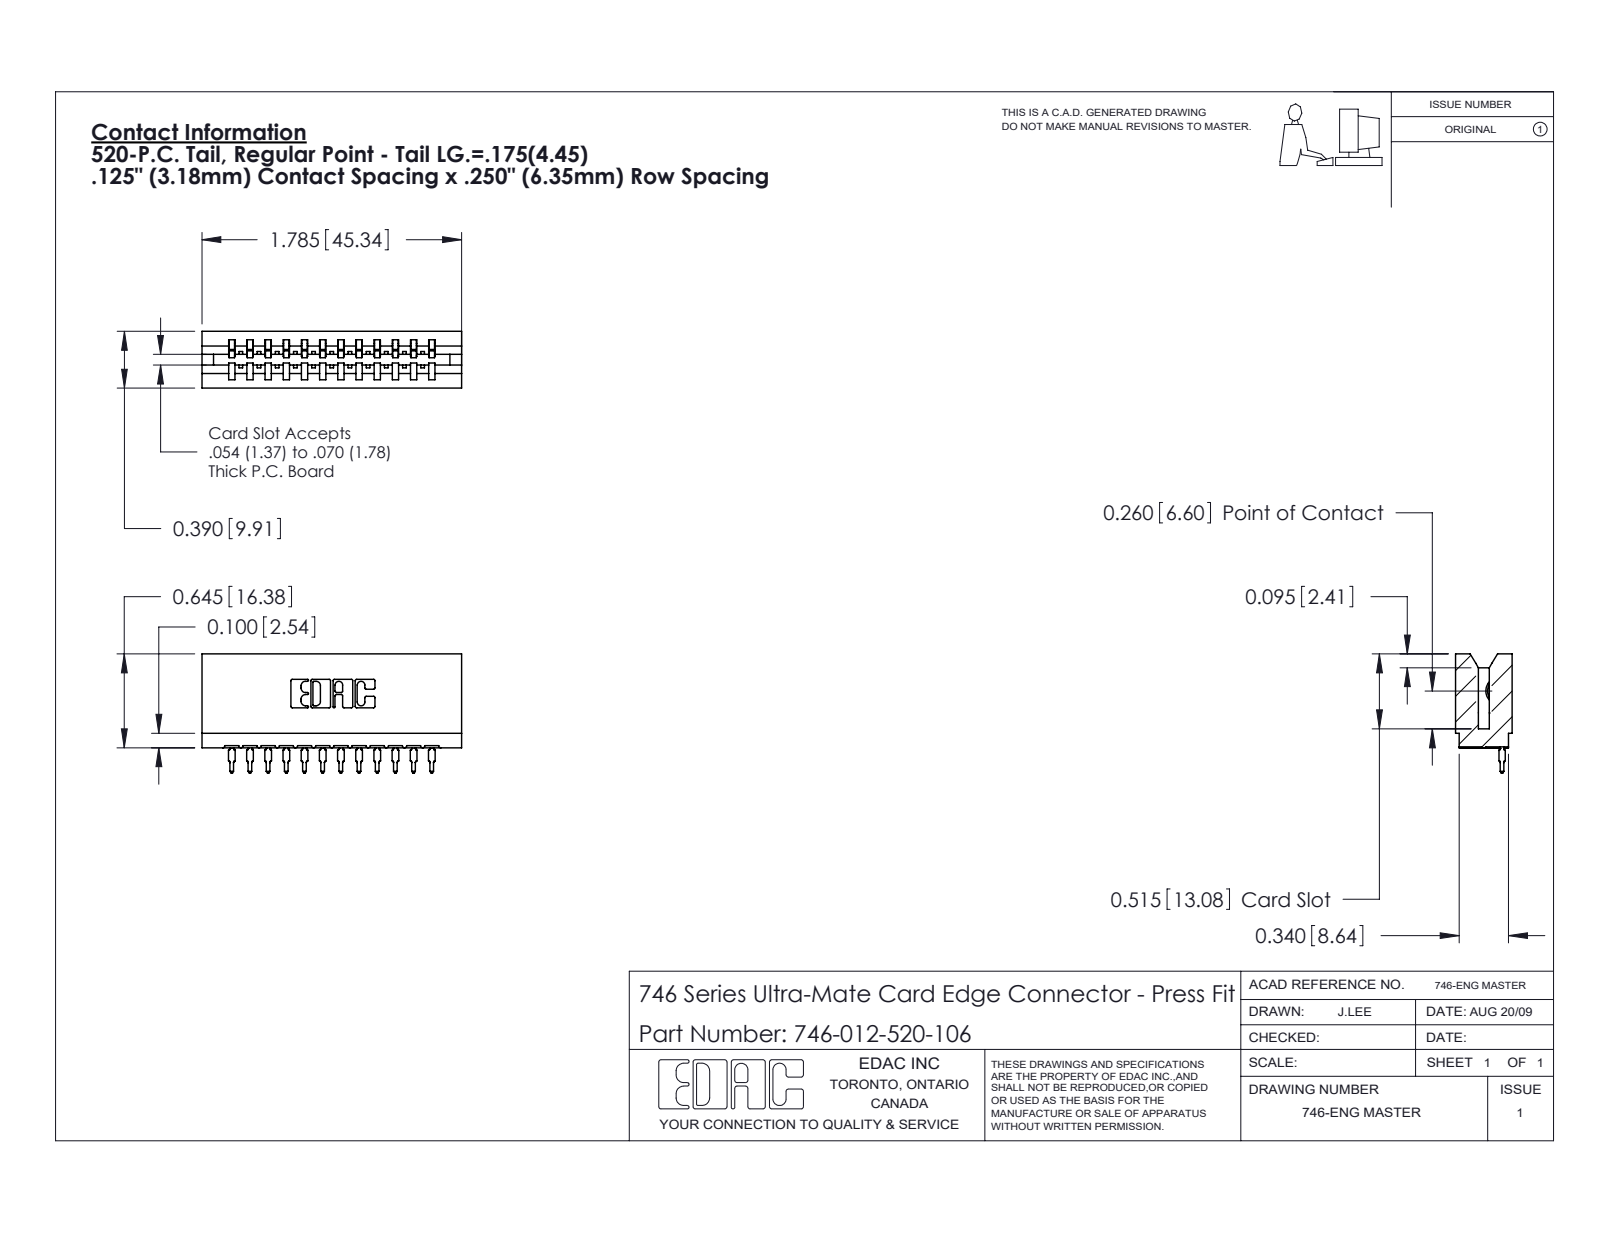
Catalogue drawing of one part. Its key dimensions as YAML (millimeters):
part_name: "746-012-520-106; 746 Part_.515 Slot Depth - 06; 746-292-001_520"
step_written_by: "SolidWorks 2020 (CONFIG_CONTROL_DESIGN)"
units: millimeters
bodies: {solids: 13, faces: 1394, planar: 812, cylindrical: 270, other: 312}
overall_size: [45.3, 20.8, 9.9]
volume: 4900
surface_area: 6690
partial_cylinders:
  - {radius: 0.5, count: 24}
  - {radius: 0.3, count: 22}
  - {radius: 0.4, count: 13}
  - {radius: 0.2, count: 6}
  - {radius: 0.8, count: 6}
  - {radius: 0.1, count: 4}
  - {radius: 0.3, count: 4}
  - {radius: 0.7, count: 3}
face_to_face_distances: [6.4, 8.5, 12.7, 1.4, 3.2, 3.2, 9.9, 1.1, 5.3, 11.6]
